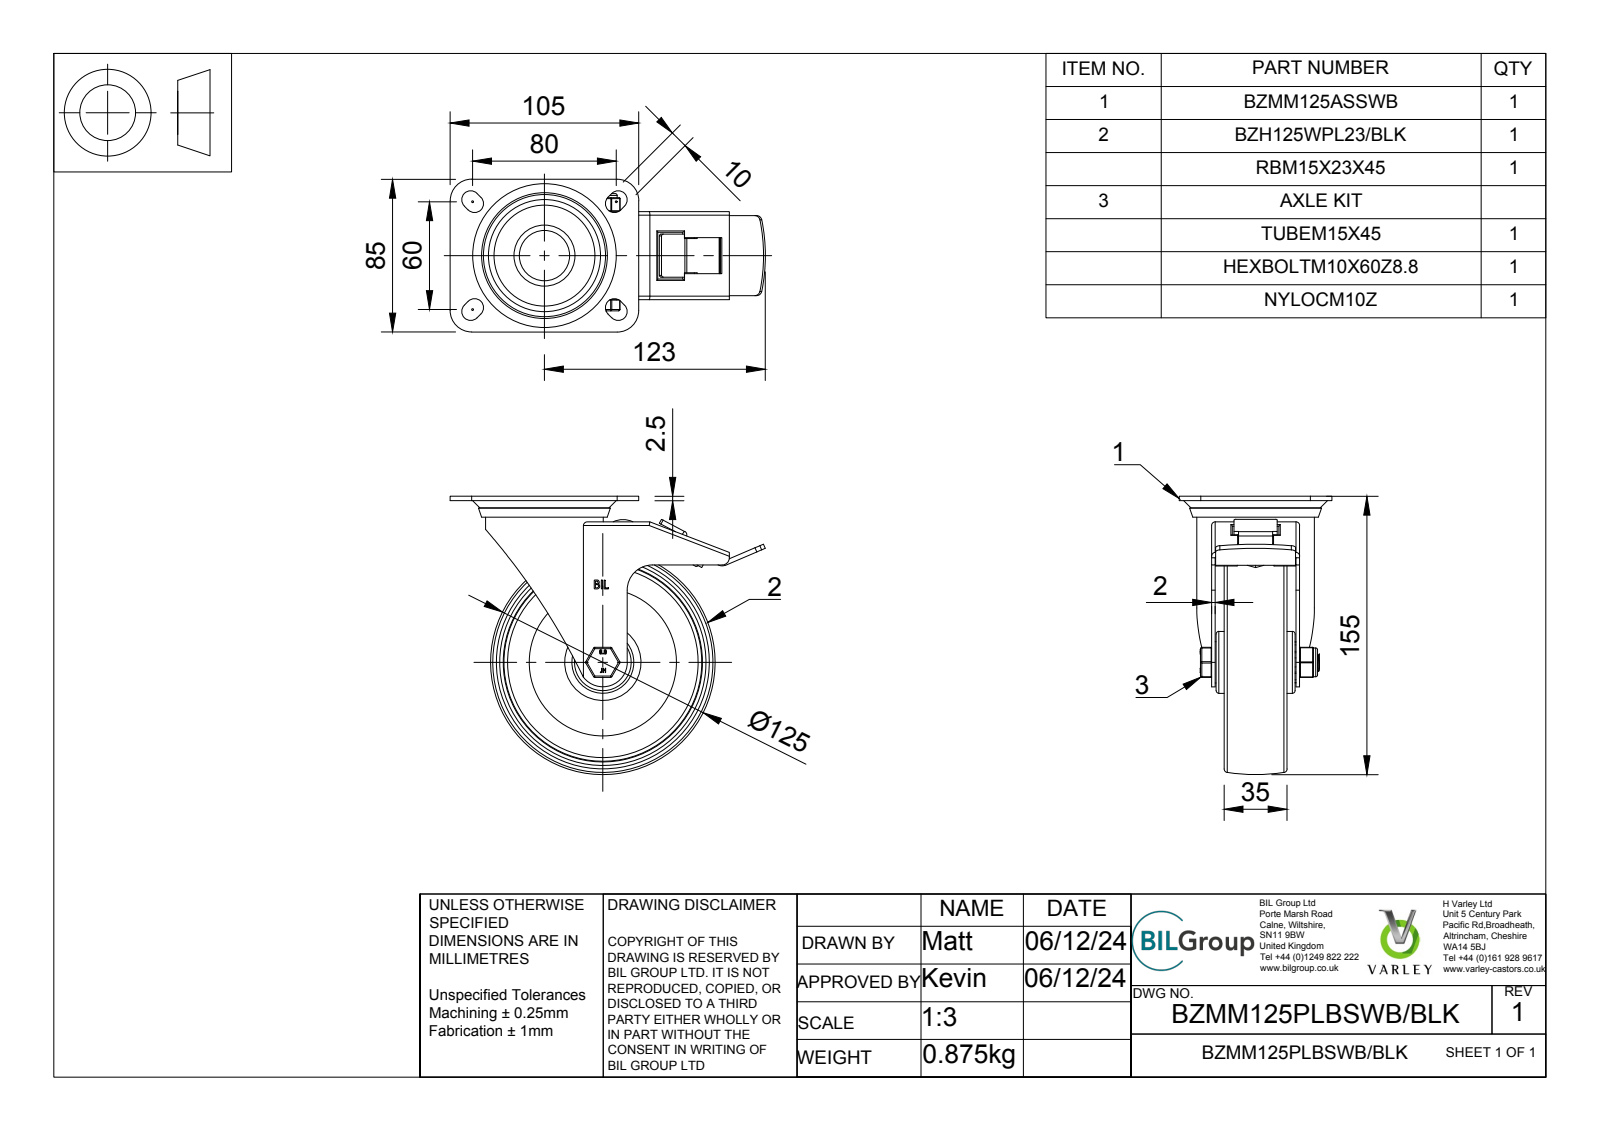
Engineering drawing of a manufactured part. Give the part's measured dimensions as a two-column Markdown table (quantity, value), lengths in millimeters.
| quantity | value |
| --- | --- |
| part name | BZMM125PLBSWB/BLK v3; BZMM125ASSWB v1; ZINC PLATED, PRESSED STEEL TOP PLATE; ZINC PLATED, PRESSED STEEL FORKS (+8 more) |
| STEP written by | Autodesk Translation Framework v13.20.0.188 (AP242_MANAGED_MODEL_BASED_3D_ENGINEERING_MIM_LF) |
| units | millimeters |
| bodies | 22 solids, 711 faces (381 planar, 225 cylindrical, 105 other) |
| overall size | 175.5 × 155 × 85 |
| volume | 271 597 mm³ |
| surface area | 146 157 mm² |
| round holes (diameter × count) | 6 × 2, 10 × 1, 10.2 × 1, 12 × 1, 15.5 × 1, 23.2 × 1, 28 × 1, 40 × 1, 61.5 × 1 |
| round bosses / shafts (diameter × count) | 4 × 8, 65.5 × 1, 34.5 × 1, 34 × 1, 23 × 1, 16 × 1, 14.95 × 1, 9.85 × 1 |
| partial cylindrical surfaces (radius × count) | 0.5 × 18, 0.75 × 16, 1.5 × 12, 5 × 9, 1 × 8, 2 × 6, 3 × 4, 12 × 4 |
| main face-to-face distances | 2, 21.75, 19.75, 25.25, 5, 27.25, 47, 7, 2.5, 9 |
| hole center spacings | 43.75 |
